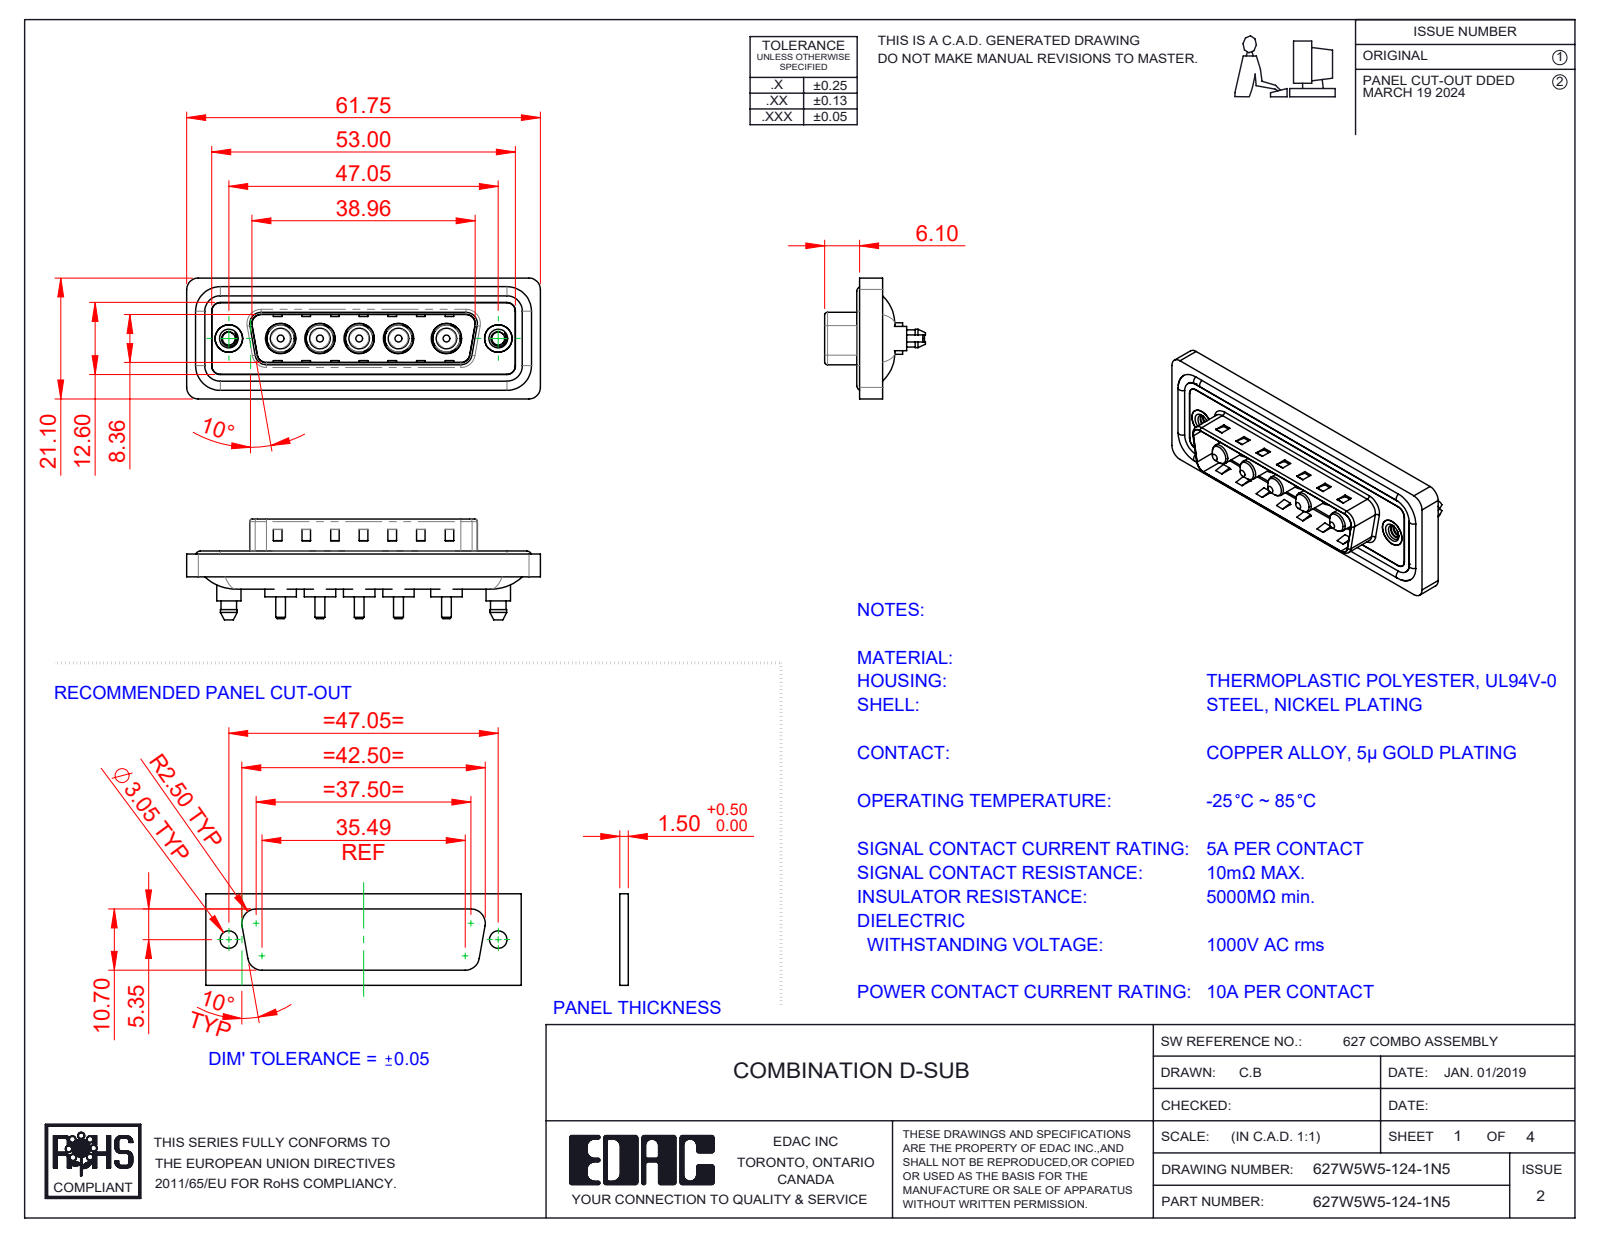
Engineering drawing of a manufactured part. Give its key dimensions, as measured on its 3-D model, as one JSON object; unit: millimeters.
{"part_name": "627Combo Housing_5W5; 627Combo Threaded Boardlock_5; 627W5W5-124-1N5; 627Combo Shell Rear_25 Contacts (+3 more)", "step_written_by": "SolidWorks 2023 (CONFIG_CONTROL_DESIGN)", "units": "millimeters", "bodies": {"solids": 17, "faces": 728, "planar": 275, "cylindrical": 315, "other": 138}, "overall_size": [61.75, 21.1, 17.6], "volume_mm3": 7533, "surface_area_mm2": 12066, "round_holes": [[4.85, 5], [5.3, 5], [2.26, 2], [4, 2], [4.8, 2], [5, 2]], "round_bosses_or_shafts": [[5.5, 5], [5.2, 5], [4.75, 5], [3.75, 5], [3.6, 5], [1.7, 5], [1.6, 4], [5.4, 2]], "partial_cylinders_radius": [[1.5, 24], [2, 18], [1.6, 10], [0.5, 8], [2.1, 5], [0.25, 4], [0.6, 4], [0.65, 4]], "face_to_face_distances": [0.4, 1.5, 1.1, 0.5, 3.1, 1.6, 2.9, 0.82, 9.58, 5.65], "hole_center_spacings": [6.86, 9.04, 13.73, 38.01, 6.87, 8.37, 8.38, 9.05]}
